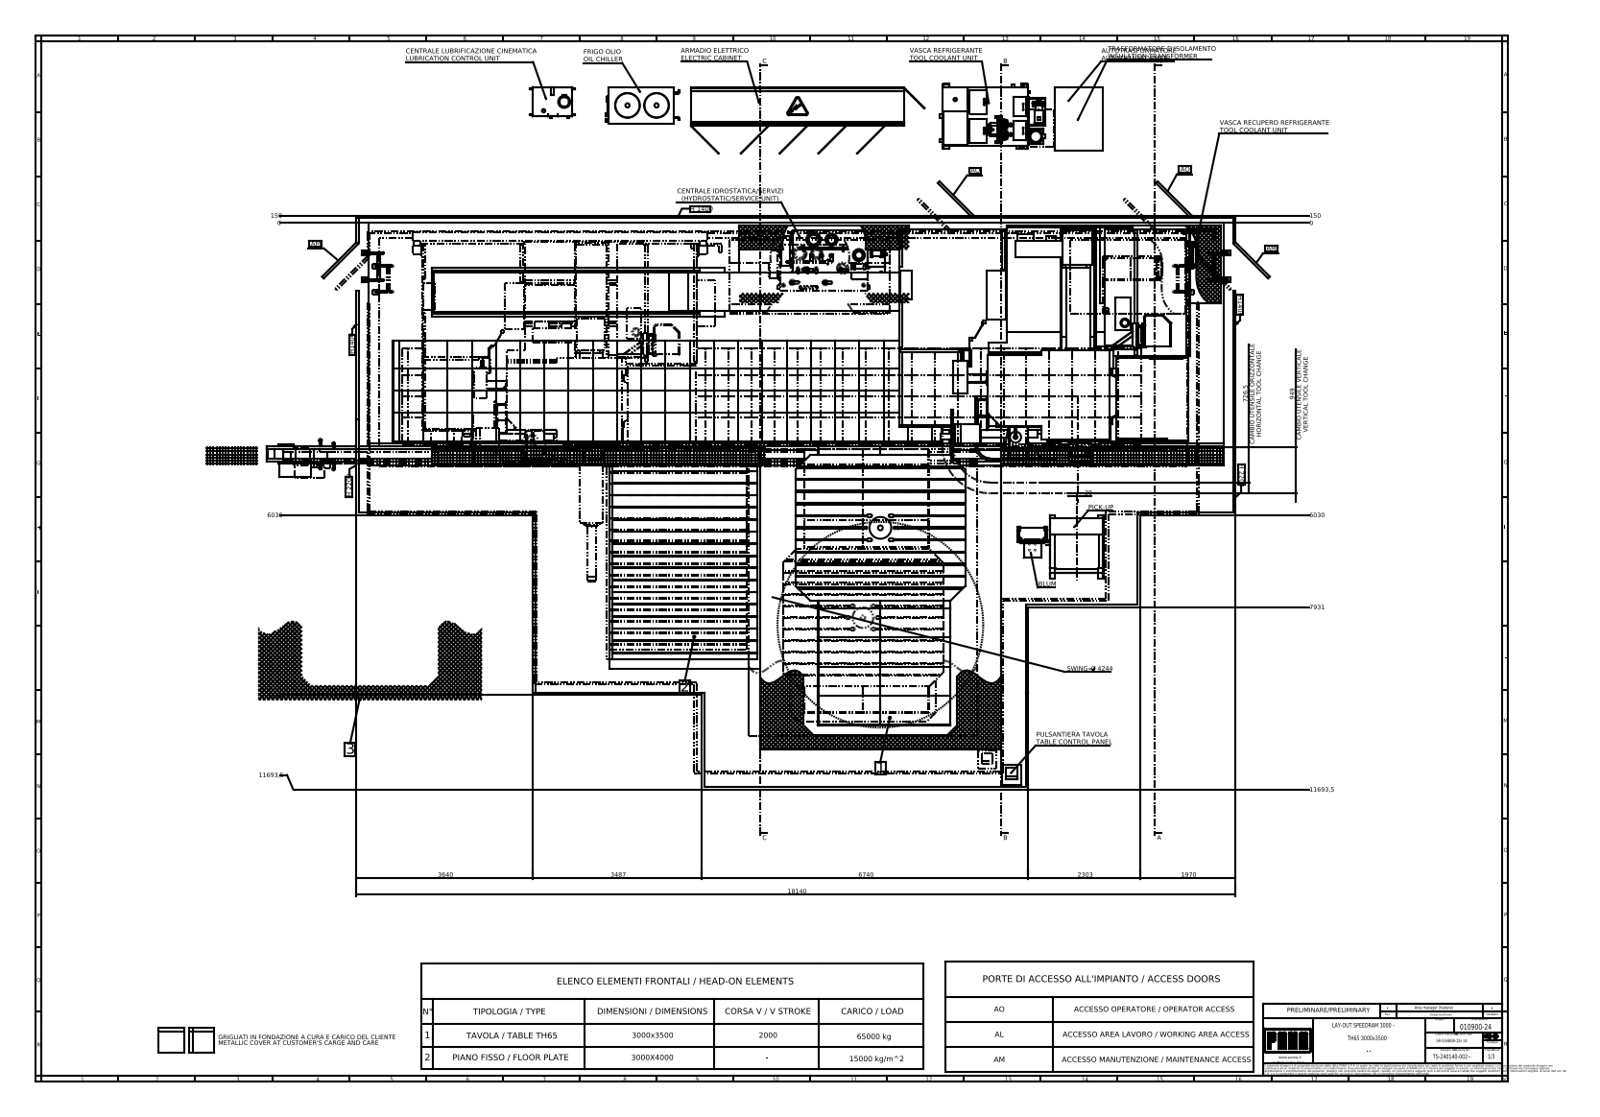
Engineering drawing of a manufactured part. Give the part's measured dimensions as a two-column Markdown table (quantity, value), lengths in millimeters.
| quantity | value |
| --- | --- |
| part name | S000047; S001805_3000x3500 (PASSO CAVA = 250) SM. 300x300; S003209_X=5000..15000; S001803_CORSA V=2000 (+8 more) |
| STEP written by | SolidWorks 2023 (AUTOMOTIVE_DESIGN) |
| units | millimeters |
| bodies | 450 solids, 7894 faces (5381 planar, 1951 cylindrical, 562 other) |
| overall size | 21640 × 17514.9 × 9961 |
| volume | 659 900 000 000 mm³ |
| surface area | 2 337 000 000 mm² |
| round holes (diameter × count) | 35 × 144, 69.6 × 63, 37.2 × 18, 5 × 17, 7 × 9, 30 × 9, 13 × 8, 14 × 8, 11 × 7, 8 × 6, 6.6 × 4, 12.5 × 4 |
| round bosses / shafts (diameter × count) | 42.4 × 18, 20 × 15, 40 × 11, 9 × 10, 55 × 8, 66.3 × 7, 60 × 6, 35 × 6 |
| partial cylindrical surfaces (radius × count) | 5 × 142, 15 × 57, 8 × 52, 10 × 35, 4 × 28, 6 × 27, 35 × 26, 20 × 24 |
| main face-to-face distances | 2000, 50, 1247, 753, 10, 17443.5, 21640, 144, 1103, 5 |
| hole center spacings | 273.13, 500, 1235.56, 758.02, 1423.59, 1000, 130, 260 |
